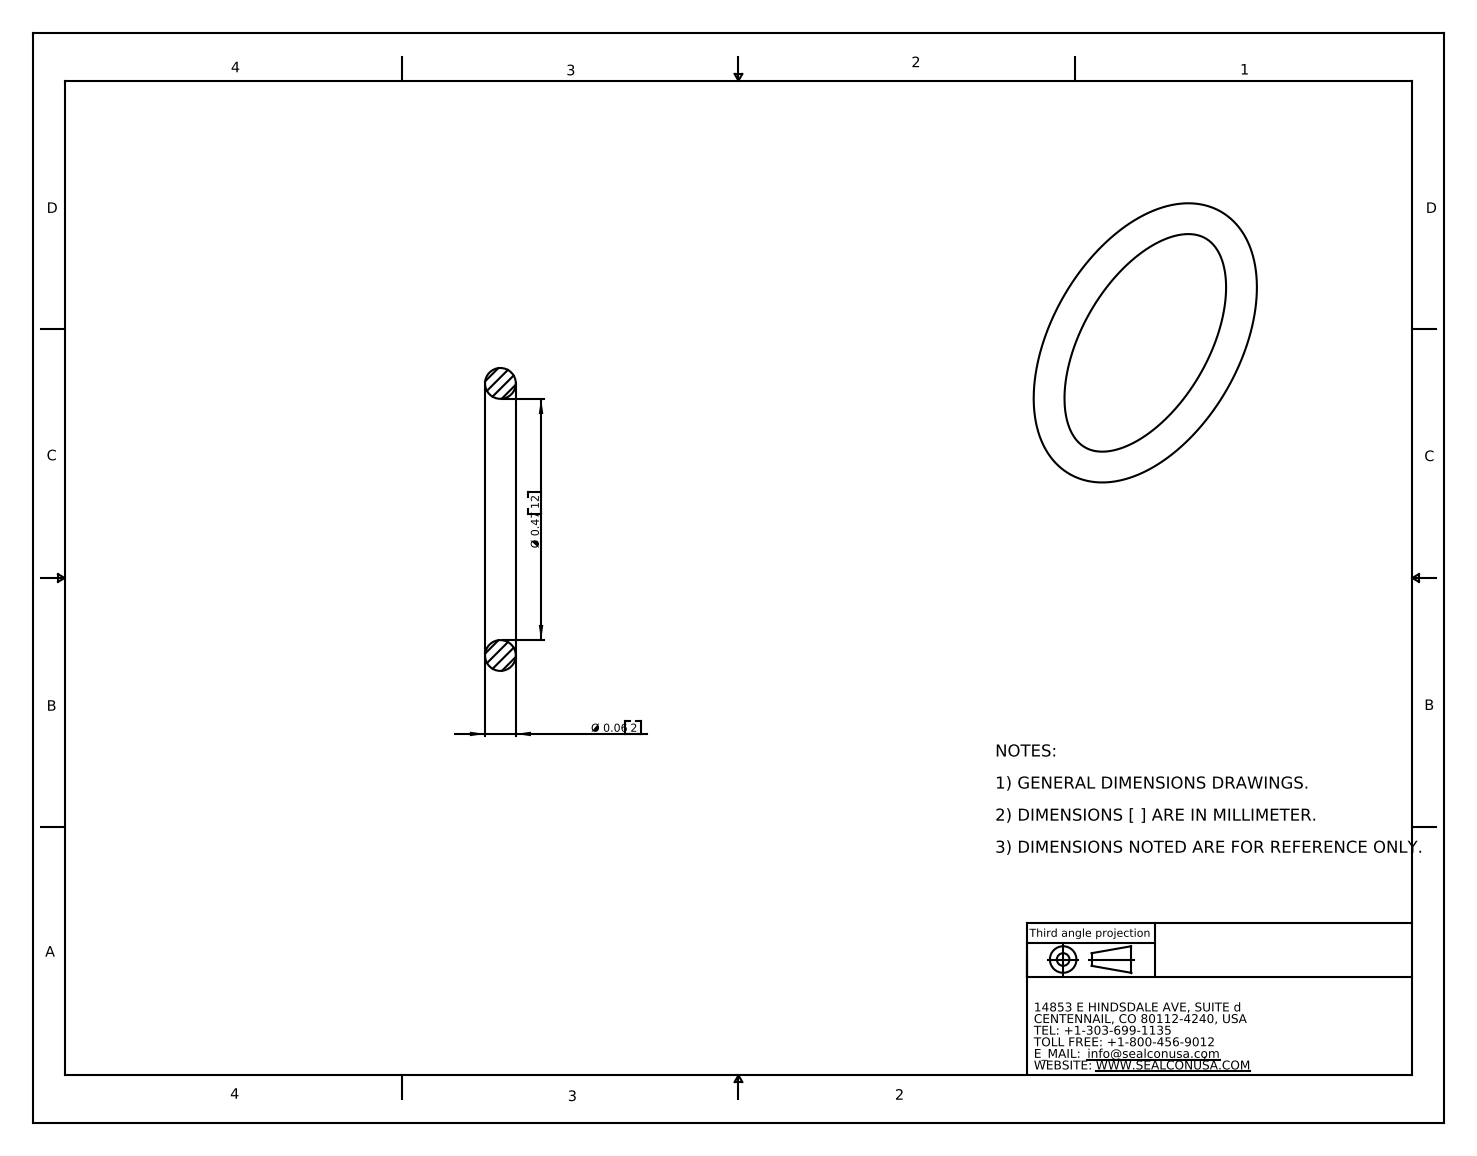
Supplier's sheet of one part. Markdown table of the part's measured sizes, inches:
| quantity | value |
| --- | --- |
| part name | OM-16-BN |
| STEP written by | SolidWorks 2007 (CONFIG_CONTROL_DESIGN) |
| units | inches |
| bodies | 1 solid, 4 faces (0 planar, 0 cylindrical, 4 other) |
| overall size | 0.59 × 0.59 × 0.06 |
| volume | 0.005 in³ |
| surface area | 0.314 in² |
